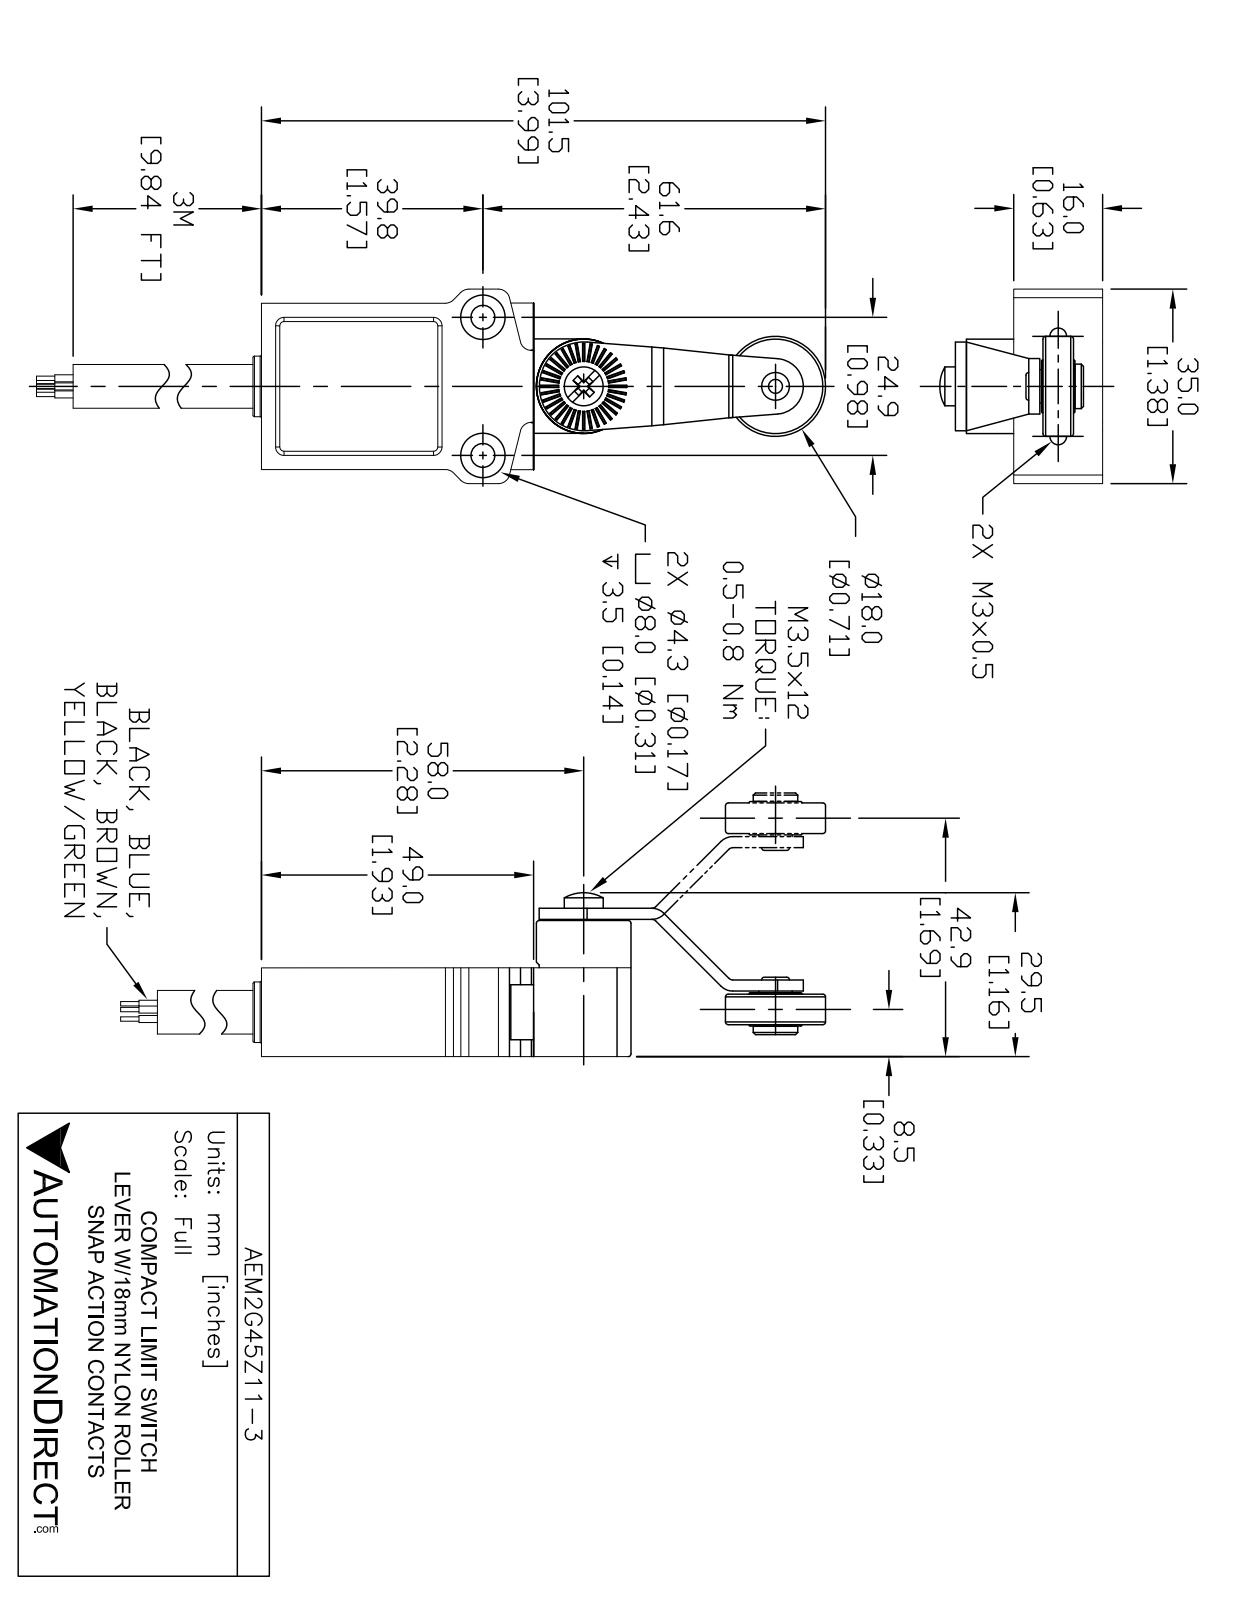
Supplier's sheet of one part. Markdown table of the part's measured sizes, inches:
| quantity | value |
| --- | --- |
| part name | AEM2G45Z11-3_Default |
| STEP written by | SolidWorks 2021 (CONFIG_CONTROL_DESIGN) |
| units | inches |
| bodies | 4 solids, 310 faces (248 planar, 51 cylindrical, 11 other) |
| overall size | 4.54 × 1.378 × 1.175 |
| volume | 1.893 in³ |
| surface area | 17.45 in² |
| round holes (diameter × count) | 0.118 × 2, 0.173 × 2, 0.323 × 2, 0.197 × 1 |
| round bosses / shafts (diameter × count) | 0.276 × 2, 0.71 × 1, 0.622 × 1, 0.31 × 1, 0.185 × 1, 0.145 × 1, 0.143 × 1 |
| partial cylindrical surfaces (radius × count) | 0.079 × 8, 0.06 × 2, 0.12 × 1, 0.14 × 1, 0.149 × 1, 0.256 × 1, 0.308 × 1 |
| main face-to-face distances | 0.63, 1.181, 0.08, 0.354, 1.929, 0.984, 0.28, 0.902, 0.434, 1.064 |
| hole center spacings | 0.863, 0.748, 0.984 |
